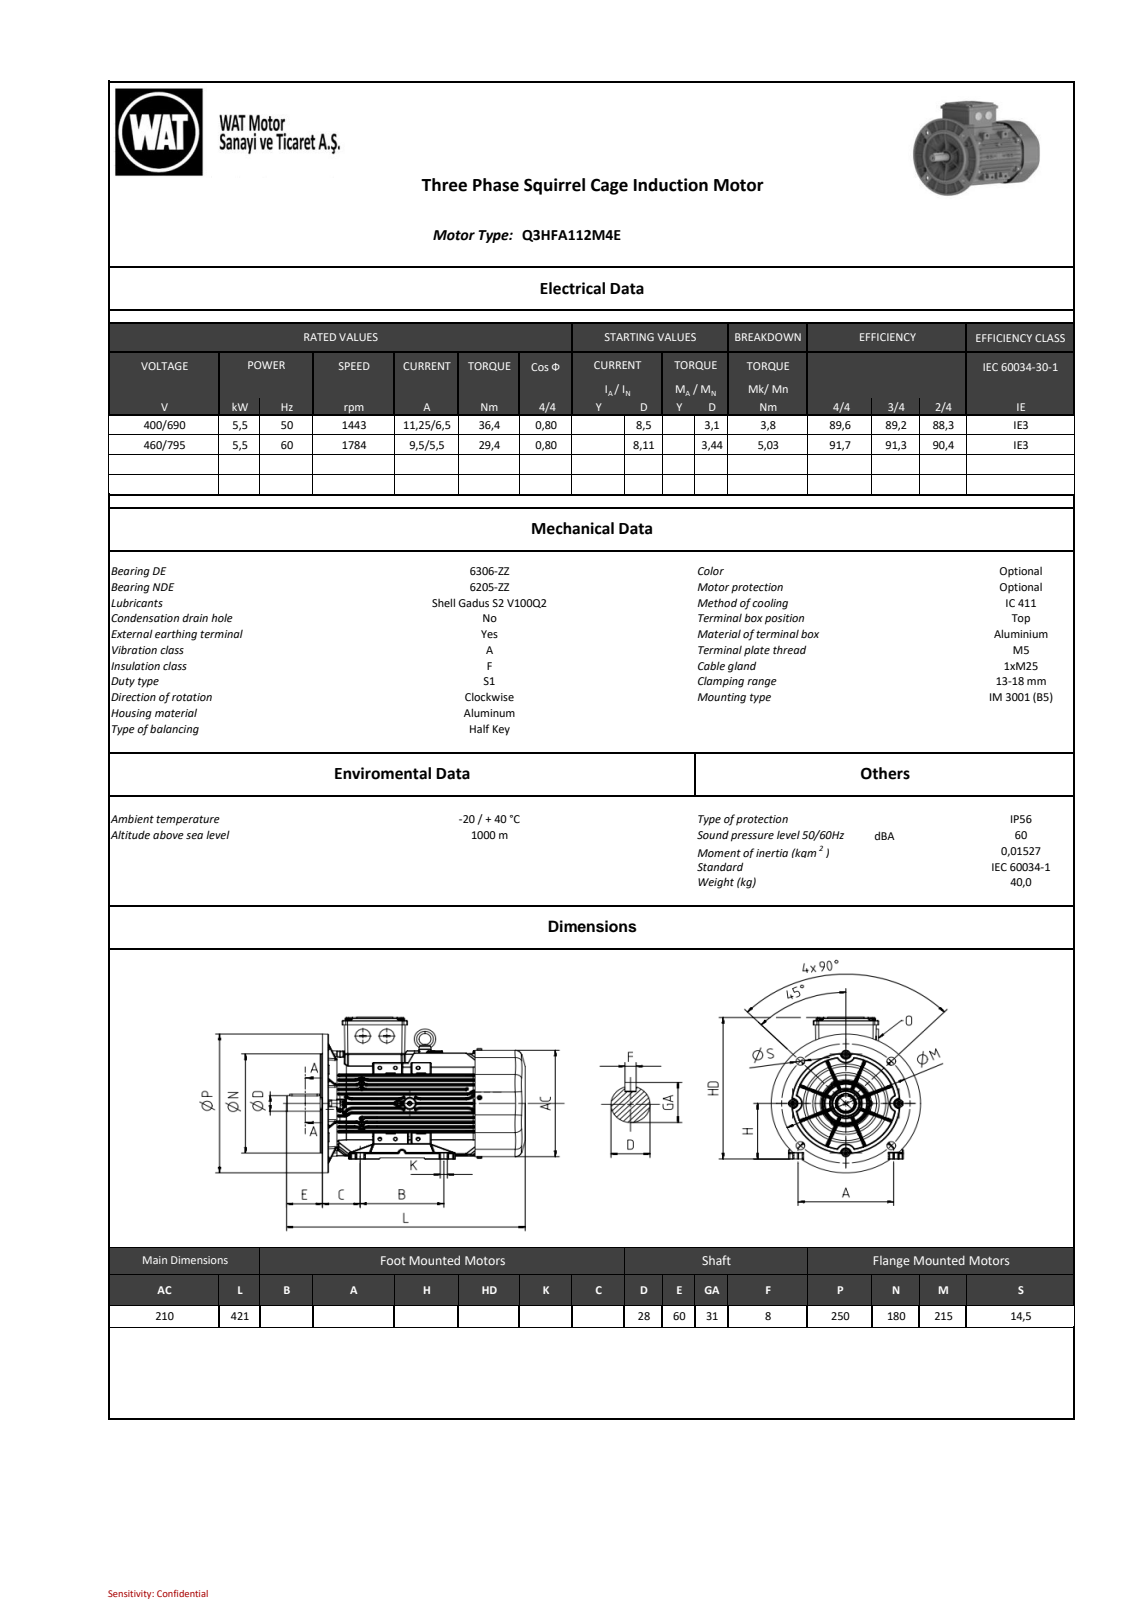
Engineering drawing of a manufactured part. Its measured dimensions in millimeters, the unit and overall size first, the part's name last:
Units: millimetres
Overall size (bounding box): 421 × 287.37 × 249.75
Round holes (diameter × count): ⌀4.6 ×2, ⌀3.5 ×1, ⌀8 ×1, ⌀8.5 ×1
Round bosses / shafts (diameter × count): ⌀8 ×6, ⌀25 ×2, ⌀188 ×1, ⌀180 ×1, ⌀35.83 ×1, ⌀30 ×1, ⌀28 ×1, ⌀6 ×1
Partial cylindrical surfaces — rounded edges, fillets, slot ends (radius × count): R2 ×605, R0.8 ×600, R1 ×395, R0.5 ×317, R3 ×169, R4 ×10, R1.75 ×8, R516.98 ×8
Main face-to-face distances: 1, 10.99, 21.5, 35.96, 99.54, 90.43, 24.97, 68.93, 112.88, 8.16
Bodies: 0 solids, 7035 faces (1462 planar, 2713 cylindrical, 2860 other)
Part name (STEP PRODUCT): QH series_ 112_B5 _DEEP COVER__stp_objects
STEP written by: SIEMENS PLM Software NX2206.8101 (AUTOMOTIVE_DESIGN)
